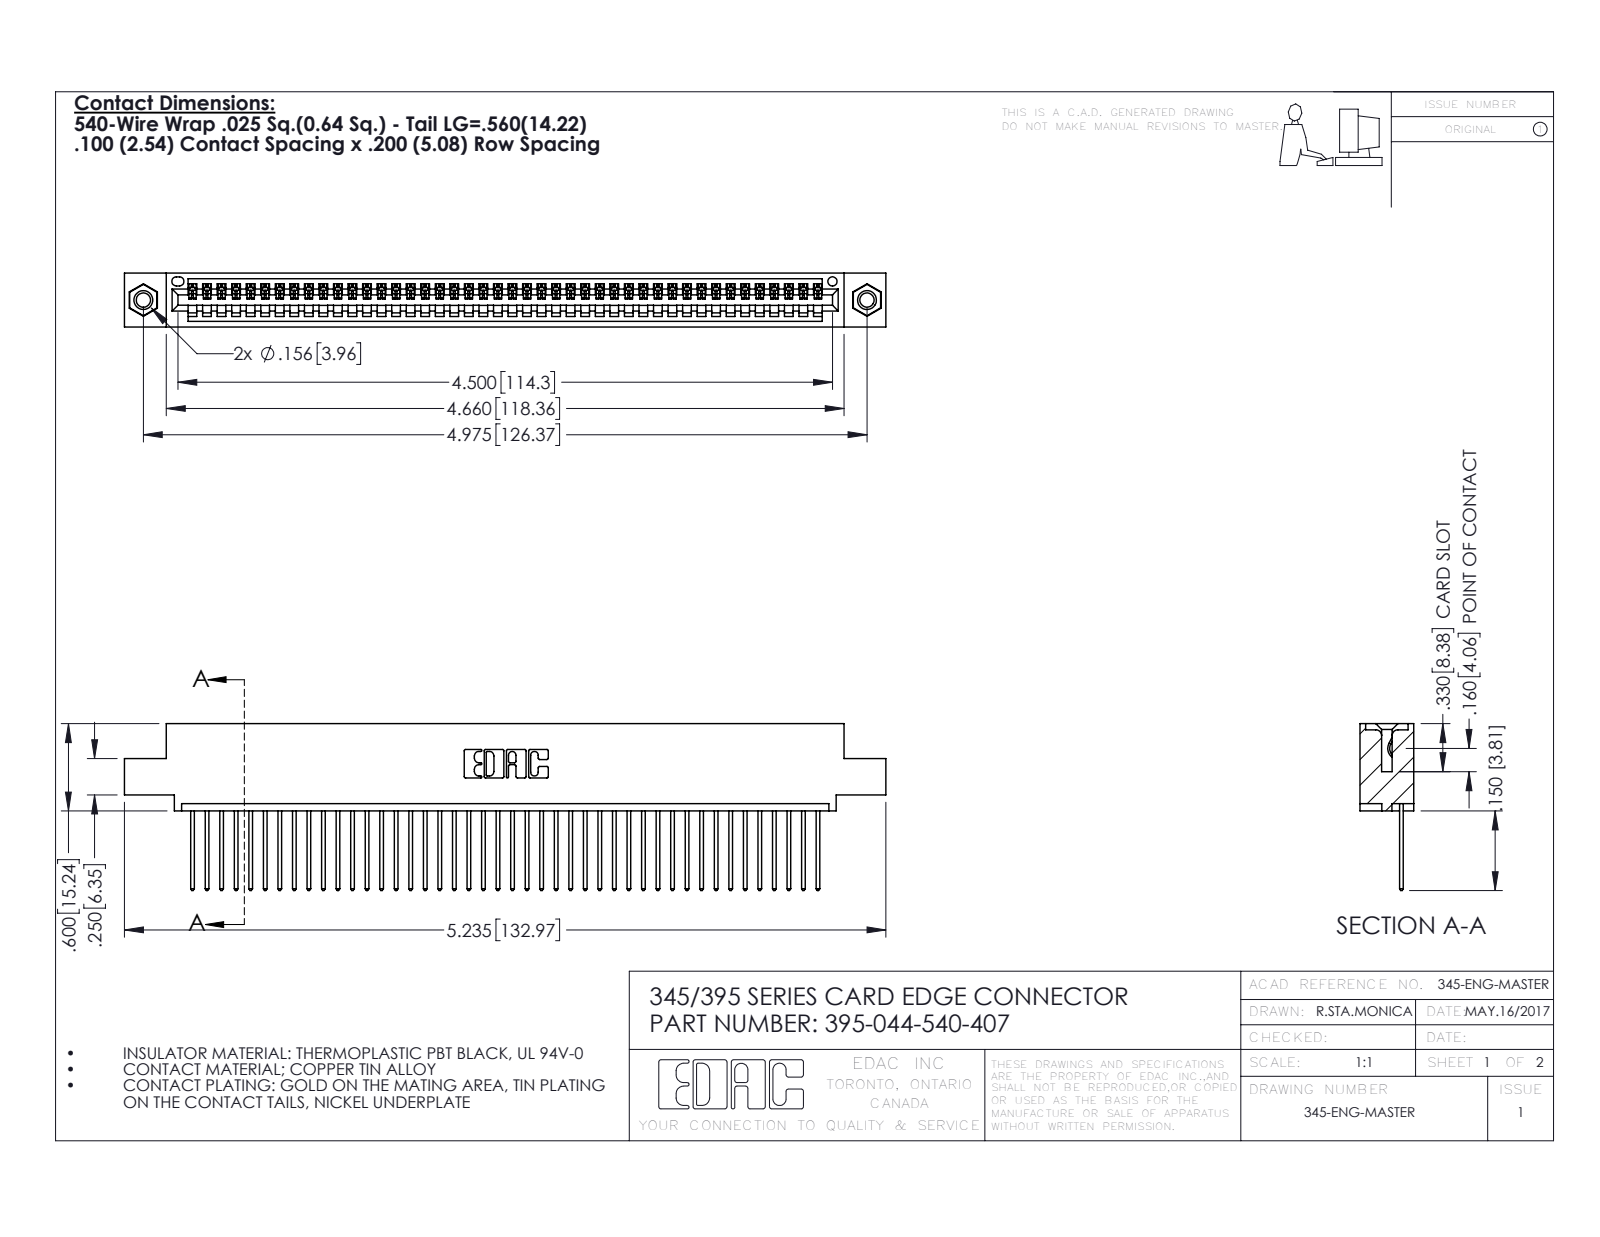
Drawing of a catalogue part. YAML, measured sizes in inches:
part_name: "345-292-001_345-293-140; 345-250-001_345-250-005-103; 345 Part_0.110 Offset - 0.156 Dia-TI; 395-044-540-407"
step_written_by: "SolidWorks 2016 (CONFIG_CONTROL_DESIGN)"
units: inches
bodies: {solids: 47, faces: 2742, planar: 1876, cylindrical: 850, other: 16}
overall_size: [5.235, 1.147, 0.37]
volume: 0.77
surface_area: 26.88
round_holes:
  - {diameter: 0.098, count: 2}
  - {diameter: 0.125, count: 2}
  - {diameter: 0.156, count: 2}
  - {diameter: 0.064, count: 1}
round_bosses_or_shafts:
  - {diameter: 0.155, count: 2}
partial_cylinders:
  - {radius: 0.006, count: 88}
  - {radius: 0.01, count: 88}
  - {radius: 0.01, count: 22}
  - {radius: 0.007, count: 6}
  - {radius: 0.031, count: 6}
  - {radius: 0.026, count: 3}
  - {radius: 0.031, count: 2}
  - {radius: 0.04, count: 2}
face_to_face_distances: [0.072, 0.298, 0.37, 0.098, 0.272, 0.025, 0.2, 0.225, 0.149, 0.072]
hole_center_spacings: [0.27, 4.739, 4.975]
